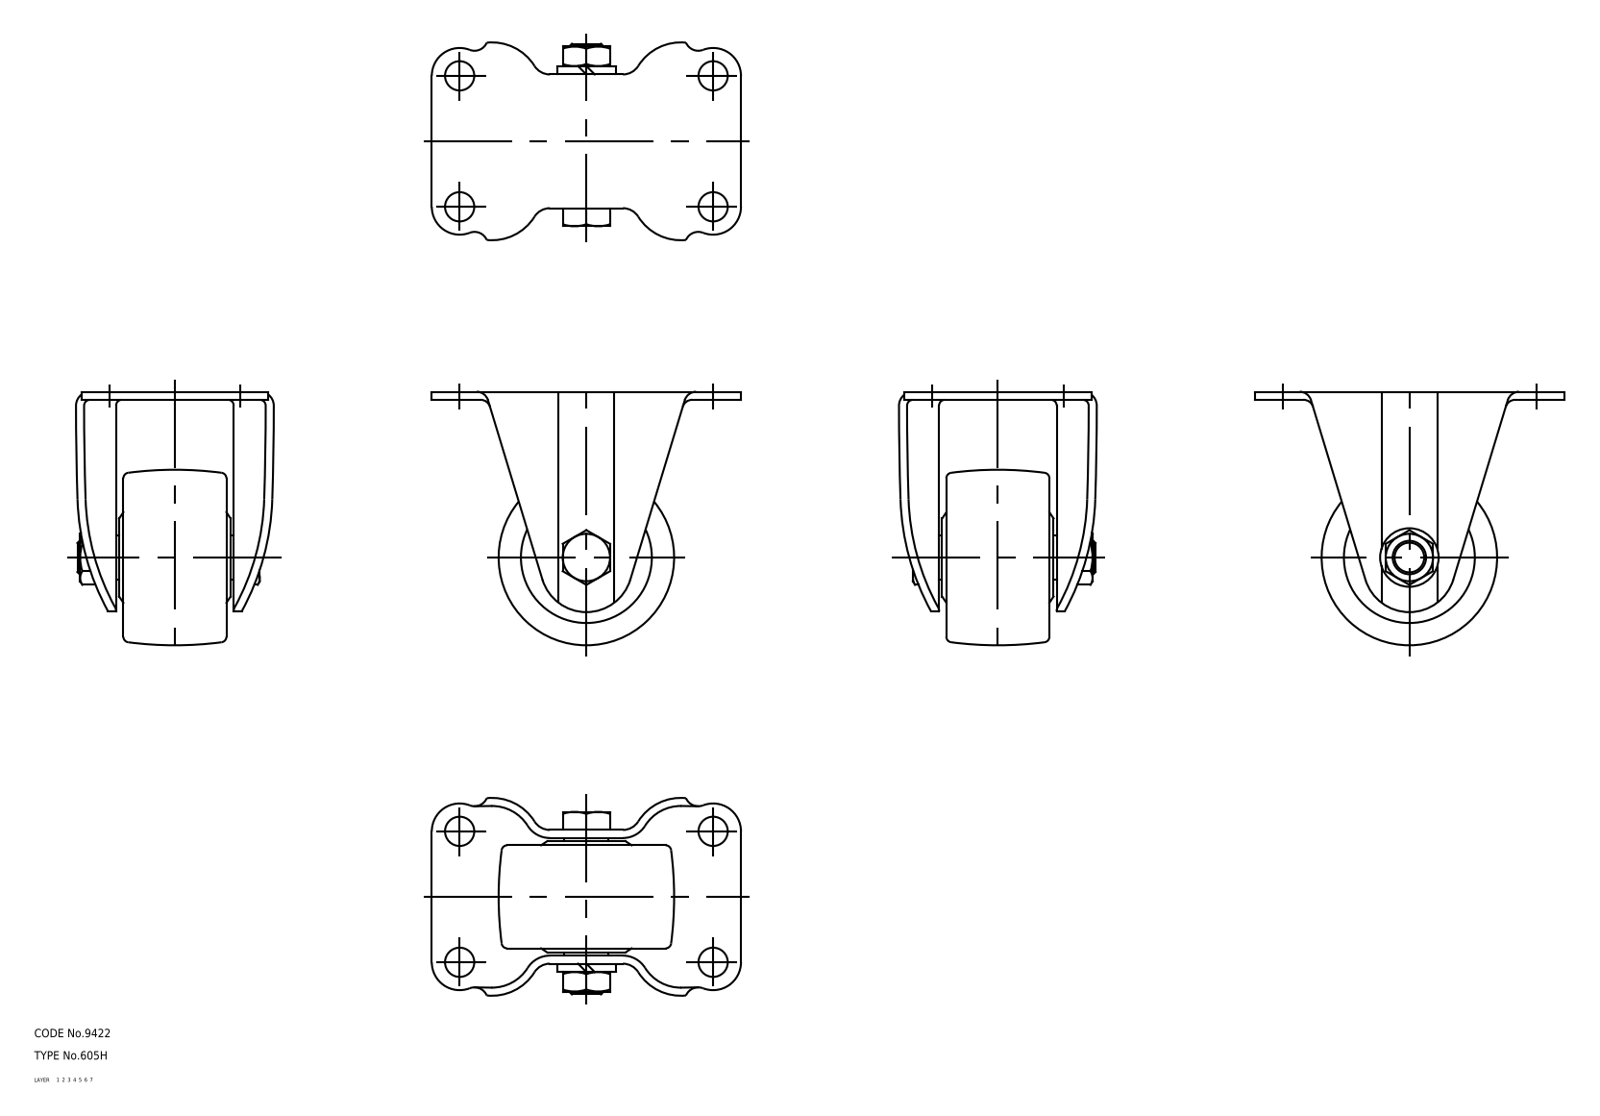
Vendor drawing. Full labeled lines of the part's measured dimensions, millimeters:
Part name (STEP PRODUCT): 67119510; 67119523; 67119536
STEP written by: CADfix (AUTOMOTIVE_DESIGN)
Units: millimetres
Bodies: 3 solids, 165 faces (0 planar, 0 cylindrical, 165 other)
Overall size (bounding box): 111 × 91 × 71
Volume: 154 211 mm³ · Surface area: 49 087 mm²
